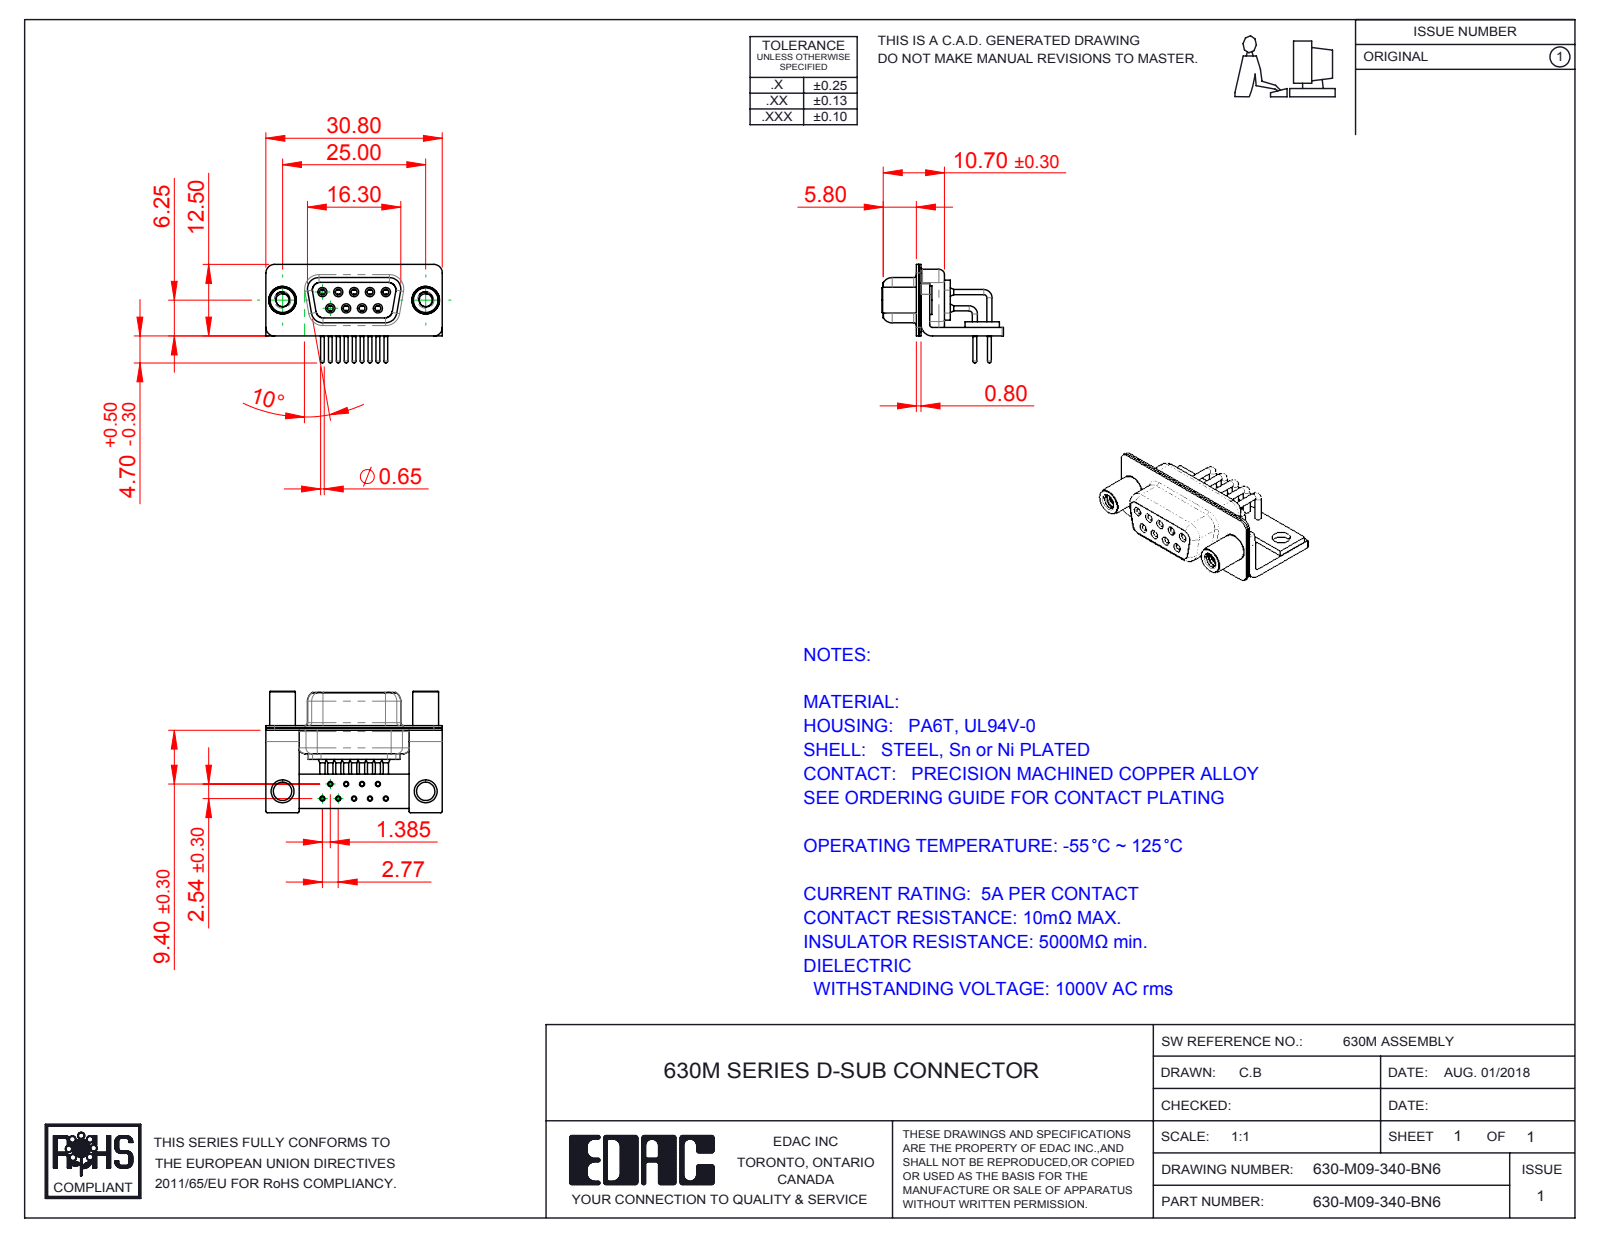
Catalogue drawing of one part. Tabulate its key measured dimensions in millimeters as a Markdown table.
| quantity | value |
| --- | --- |
| part name | 630M Housing_09 Contacts; 630-M09-340-BN6; 630M Stabilizer Board_09 Contacts; 630M Shell Rear_09 Contacts (+5 more) |
| STEP written by | SolidWorks 2016 (CONFIG_CONTROL_DESIGN) |
| units | millimeters |
| bodies | 17 solids, 874 faces (230 planar, 426 cylindrical, 218 other) |
| overall size | 30.8 × 21.2 × 17.2 |
| volume | 2 318 mm³ |
| surface area | 5 995 mm² |
| round holes (diameter × count) | 0.9 × 9, 1 × 9, 1.1 × 9, 1.7 × 9, 1.8 × 9, 2 × 9, 2.26 × 2, 3.2 × 2, 4 × 2, 4.8 × 2 |
| round bosses / shafts (diameter × count) | 1.6 × 9, 1.5 × 9, 0.9 × 9, 0.65 × 9, 5 × 2, 4.9 × 2, 4.5 × 2 |
| partial cylindrical surfaces (radius × count) | 0.25 × 16, 1.5 × 16, 2 × 13, 1.35 × 8, 1.6 × 8, 0.5 × 5, 0.6 × 4, 0.65 × 4 |
| main face-to-face distances | 0.4, 0.8, 1.5, 2.3, 1.9, 1, 9.35, 1.45, 8.5, 8.95 |
| hole center spacings | 2.77, 5.54, 3.16, 4.87, 8.31, 2.89, 2.9, 5.03 |
